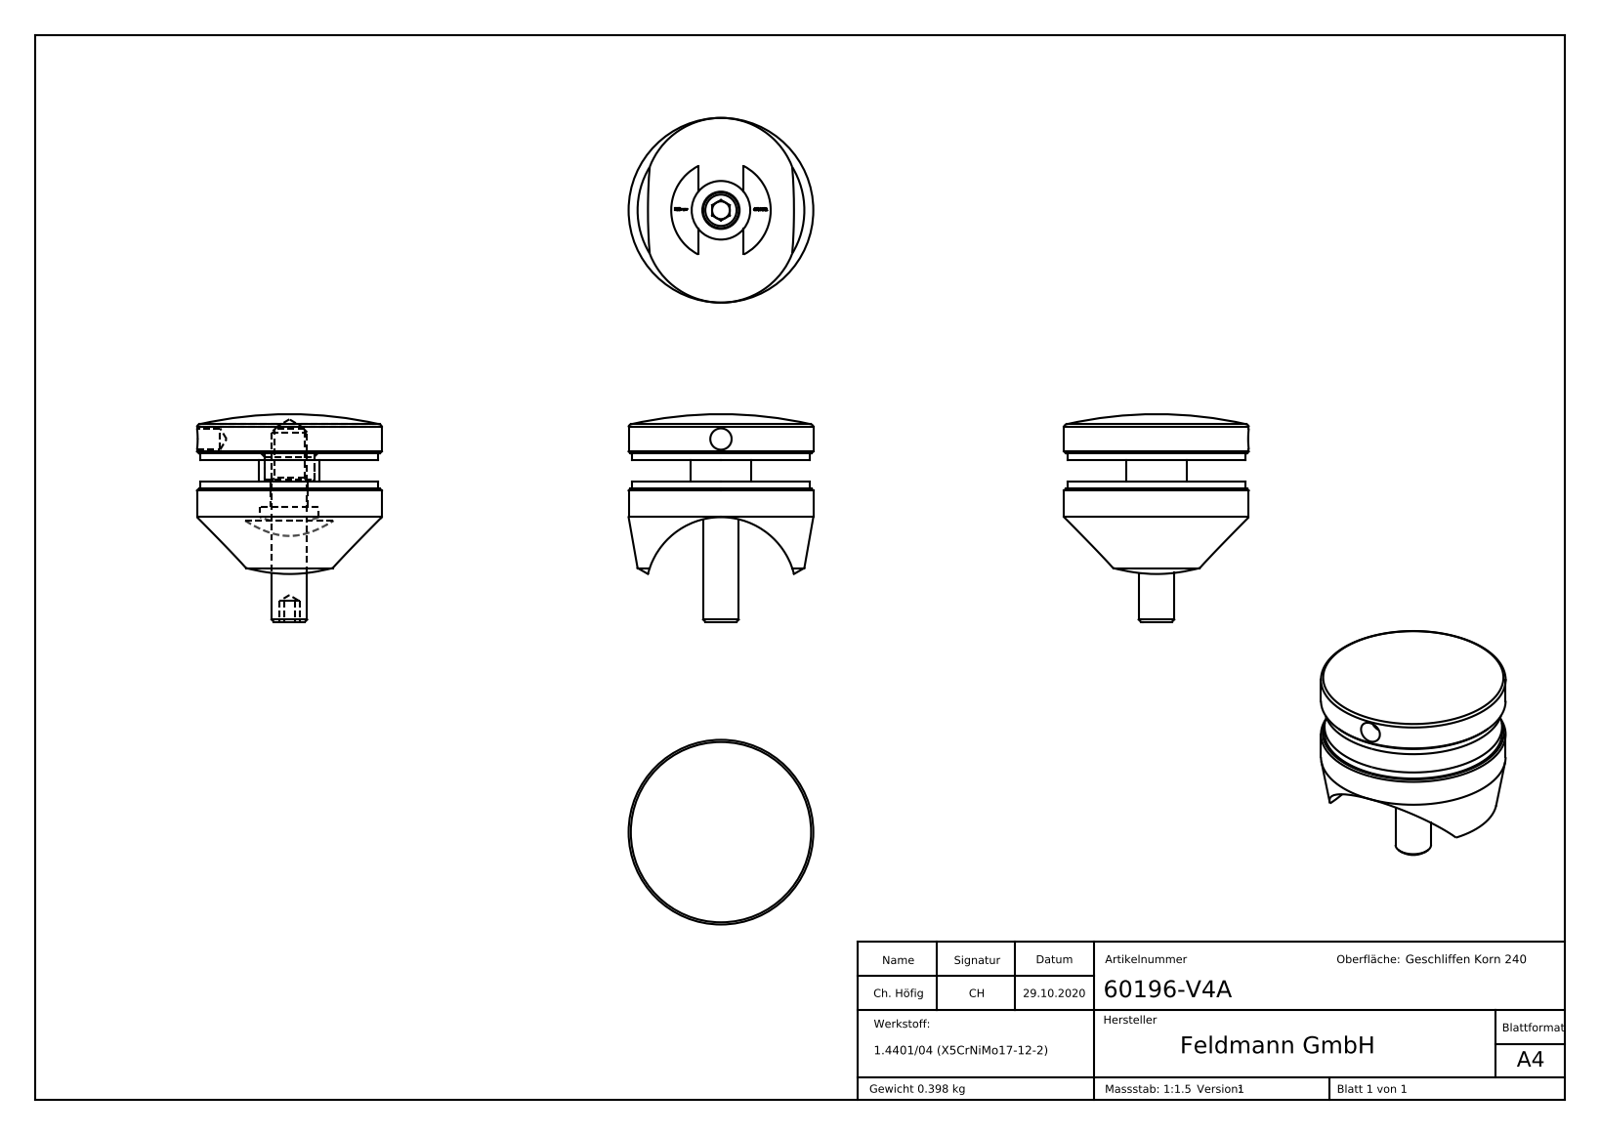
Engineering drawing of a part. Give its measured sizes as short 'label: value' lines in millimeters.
name: 6019X-240 Konfig Teil2; 6019X-240 Konfig Teil1; 60196-V4A; 6019X-240 Konfig Teil3_6019X-XXX Teil3 (+7 more)
written by: SolidWorks 2018 (CONFIG_CONTROL_DESIGN)
unit: mm
bodies: 5 solids, 299 faces (155 planar, 29 cylindrical, 115 other)
size: 110 × 52 × 52
volume: 56 405 mm³; area: 24 397 mm²
holes: 1× ⌀6, 1× ⌀8.5, 1× ⌀10.5, 1× ⌀14, 1× ⌀16.5
bosses: 1× ⌀52, 1× ⌀50, 1× ⌀17, 1× ⌀10
rounds: 1× R14, 1× R21.2
face distances: 2, 8, 10, 6, 9, 11, 17, 19, 5, 4
